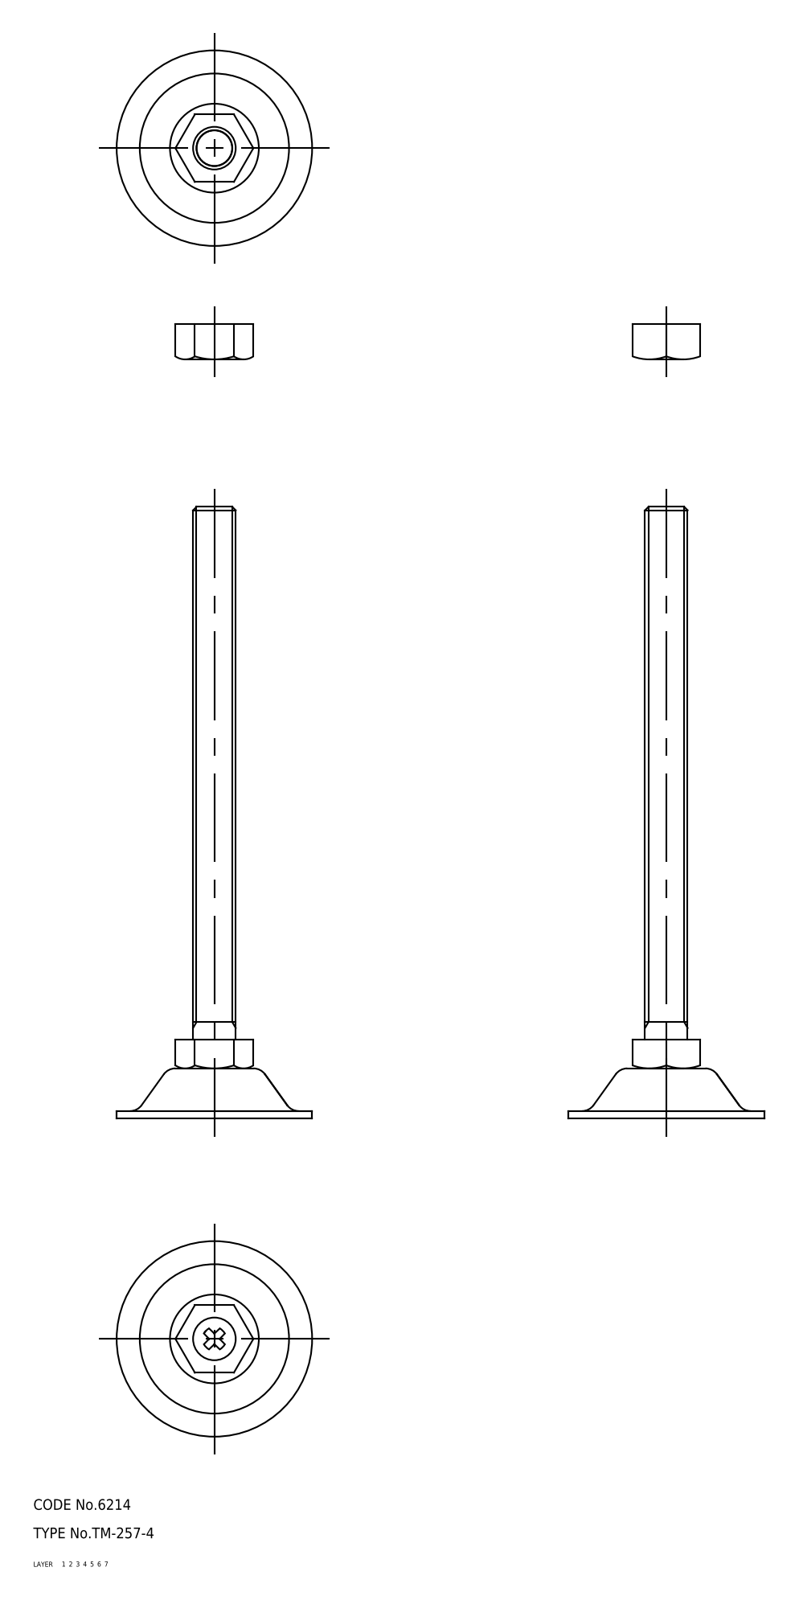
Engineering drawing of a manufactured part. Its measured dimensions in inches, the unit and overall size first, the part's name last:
Units: inches
Overall size (bounding box): 6.772 × 2.165 × 2.165
Volume: 1.861 in³ · Surface area: 25.18 in²
Bodies: 4 solids, 95 faces (0 planar, 0 cylindrical, 95 other)
Part name (STEP PRODUCT): nut; foot; bolt; TM_257_4_9822_36
STEP written by: CADfix (AUTOMOTIVE_DESIGN)
